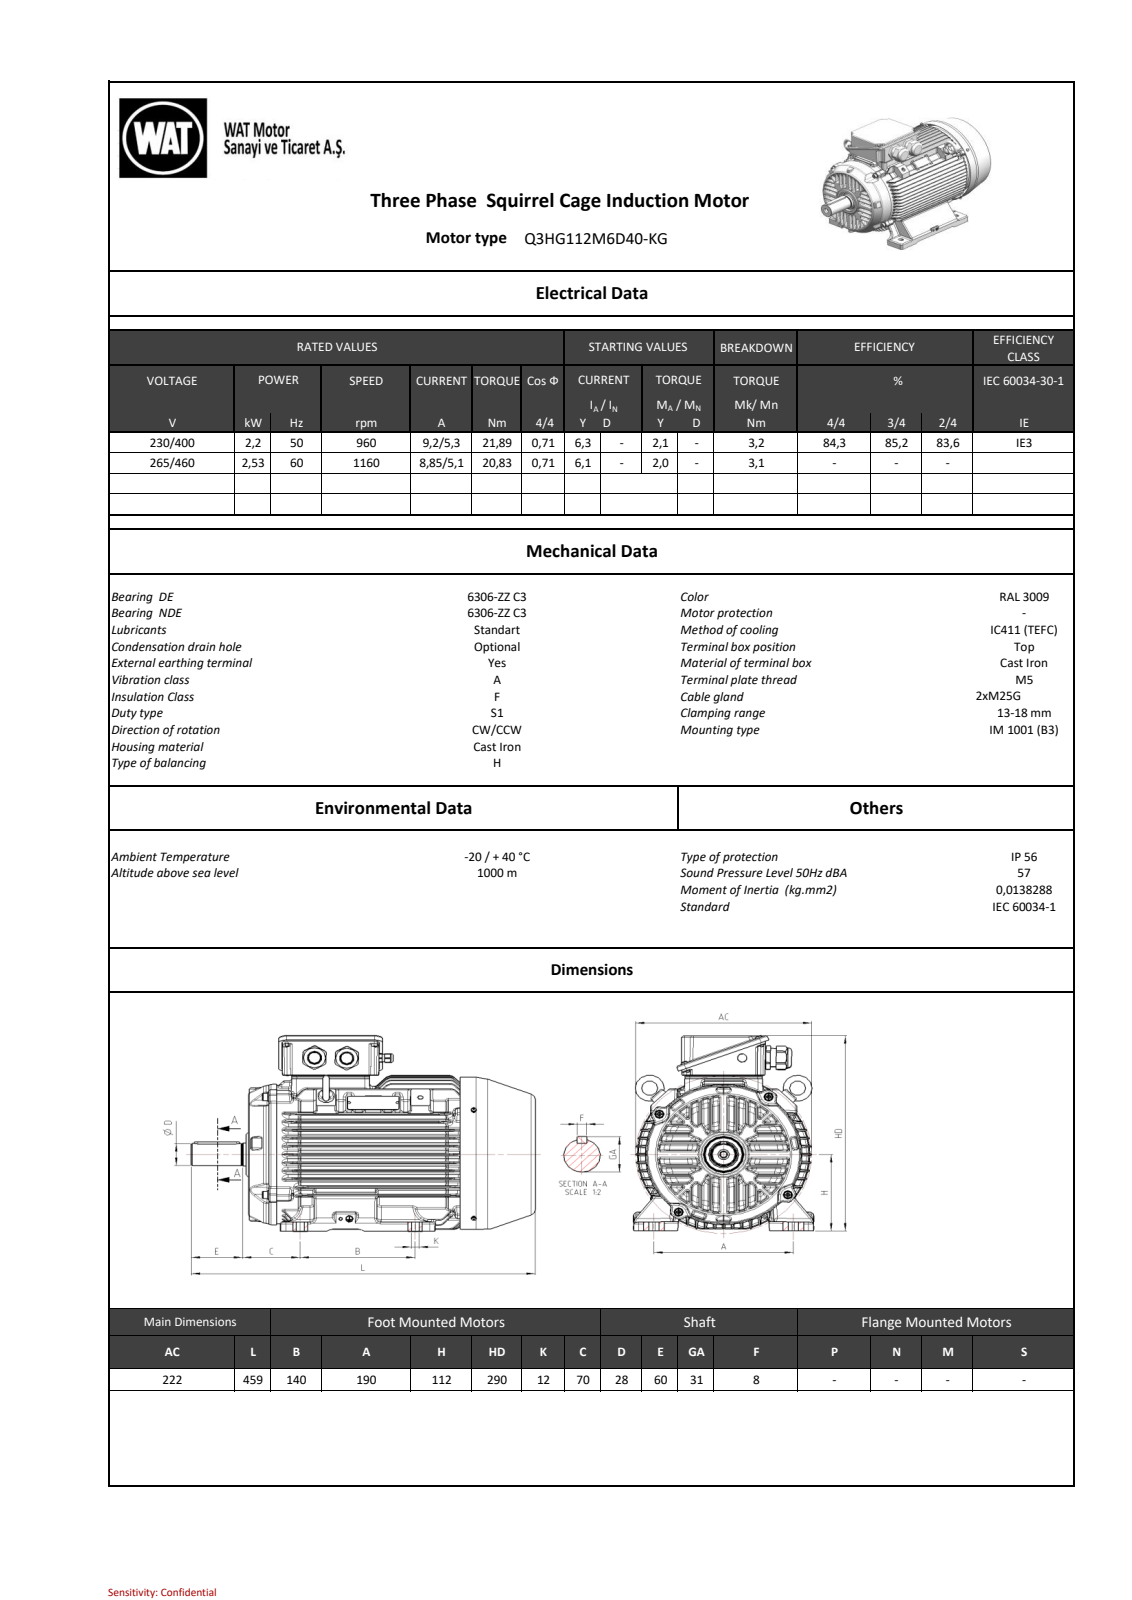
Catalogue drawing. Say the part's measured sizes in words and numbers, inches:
The part is named "260037F440EAov8i". Its 3-D file was written by "SIEMENS PLM Software NX 11.0 (AUTOMOTIVE_DESIGN)". It is 0 solids with 5466 faces: 1034 planar, 1584 cylindrical and 2848 other. Overall it measures 18.051 by 11.413 by 9.803 inches. Round holes: 9 of diameter 0.197, 6 of diameter 0.177, 2 of diameter 0.098, 2 of diameter 0.13, 2 of diameter 0.268, 2 of diameter 0.394, 2 of diameter 0.677, 1 of diameter 0.138, 1 of diameter 0.157, 1 of diameter 0.315, 1 of diameter 0.335, 1 of diameter 0.413. Round bosses or shafts: 4 of diameter 0.394, 4 of diameter 0.236, 2 of diameter 1.091, 2 of diameter 0.994, 2 of diameter 0.787, 1 of diameter 8.465, 1 of diameter 7.559, 1 of diameter 1.575. Partial cylindrical surfaces (rounded edges, fillets, slot ends): 284 of radius 0.157, 165 of radius 0.118, 126 of radius 0.02, 96 of radius 0.059, 49 of radius 0.197, 47 of radius 0.079, 39 of radius 0.039, 24 of radius 0.071. The main face-to-face distances are 0.516, 1.035, 0.519, 1.573, 3.565, 1.557, 1.041, 0.522, 3.046, 2.53. The hole center spacings are 3.819, 4.528, 5.401, 1.326, 4.041, 4.381, 6.069, 6.257.
